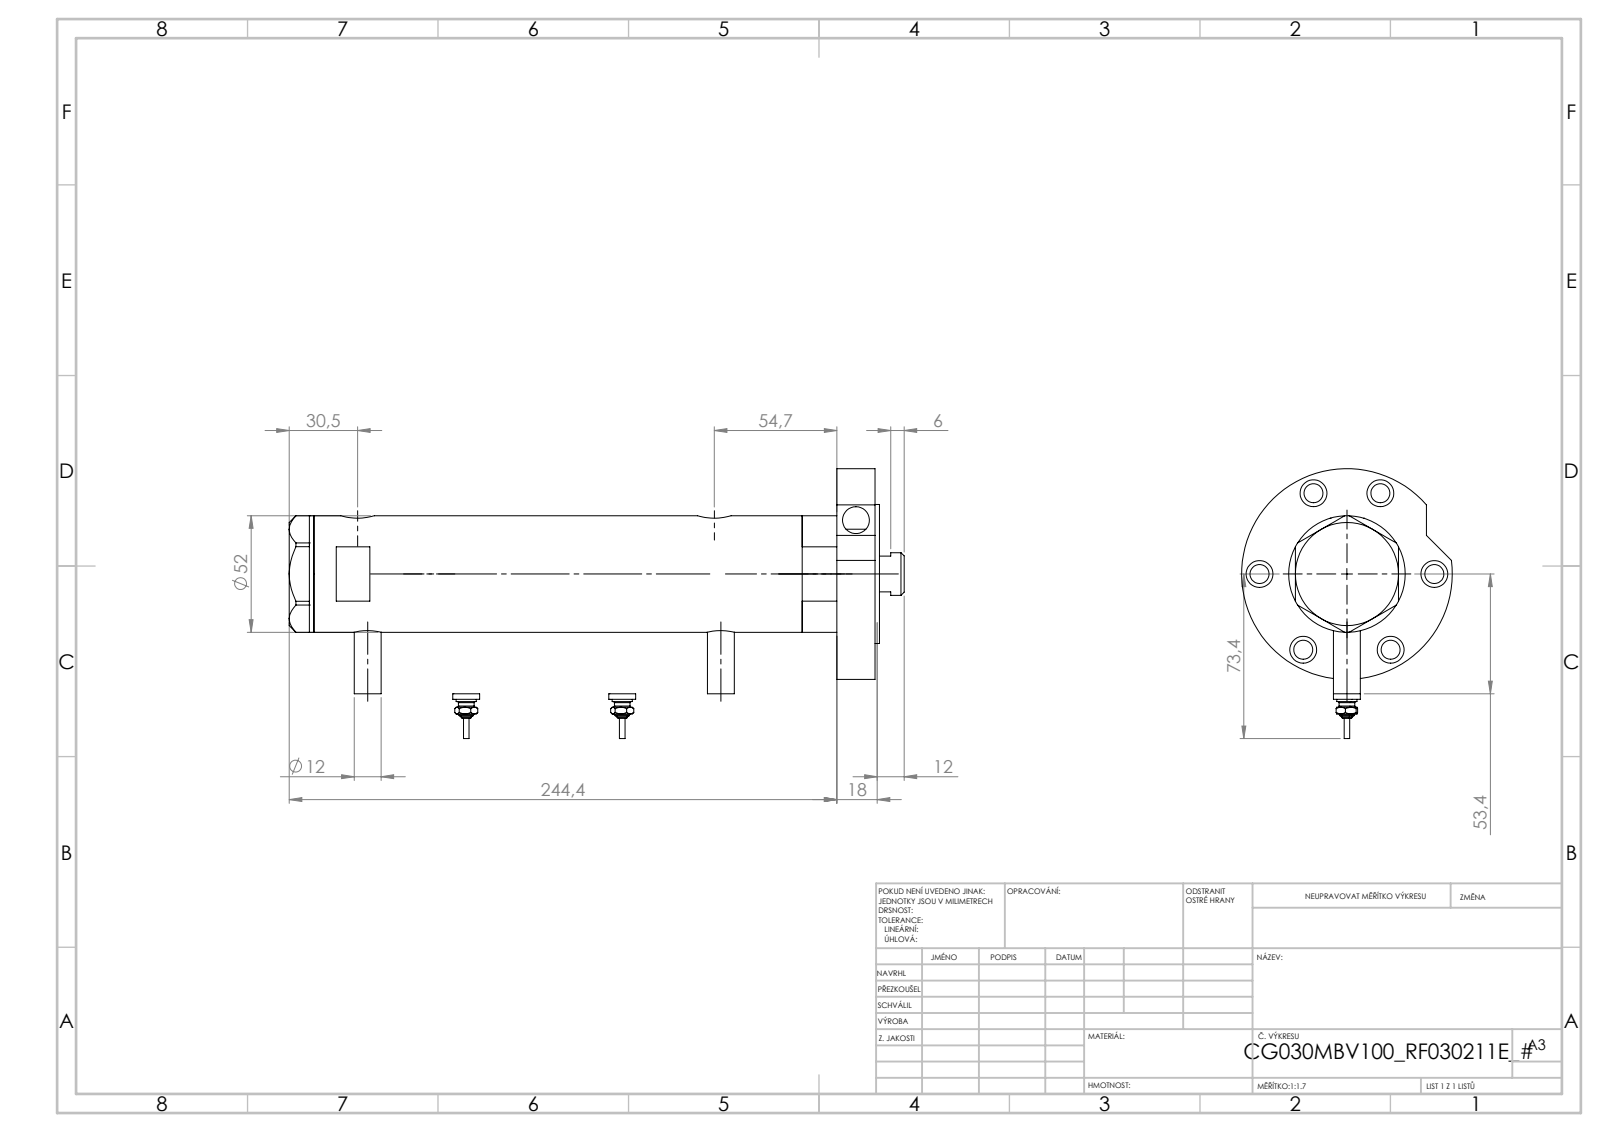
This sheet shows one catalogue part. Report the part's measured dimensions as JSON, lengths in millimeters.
{"part_name": "V270CG_BACK; V270CG_RF211E; V270CG_SWITCH; V270CG_FRONT (+2 more)", "step_written_by": "SolidWorks 2019 (CONFIG_CONTROL_DESIGN)", "units": "millimeters", "bodies": {"solids": 7, "faces": 290, "planar": 106, "cylindrical": 110, "other": 74}, "overall_size": [249.02, 105.3, 94], "volume_mm3": 525288, "surface_area_mm2": 122862, "round_holes": [[12, 7], [8.5, 6], [5, 2], [9.73, 2], [12.5, 2], [15, 2], [6.5, 1], [20, 1], [21.5, 1], [30, 1], [33, 1], [40, 1]], "round_bosses_or_shafts": [[12, 3], [9, 2], [7, 2], [4.34, 2], [2.4, 2], [94, 1], [62, 1], [52, 1]], "face_to_face_distances": [17, 205.44, 222.44, 51.9, 2, 224.44, 153.54, 68.9, 70.9, 19], "hole_center_spacings": [39, 2.9, 4.5, 43.34, 64.85, 67.55, 69.95, 77.83]}
